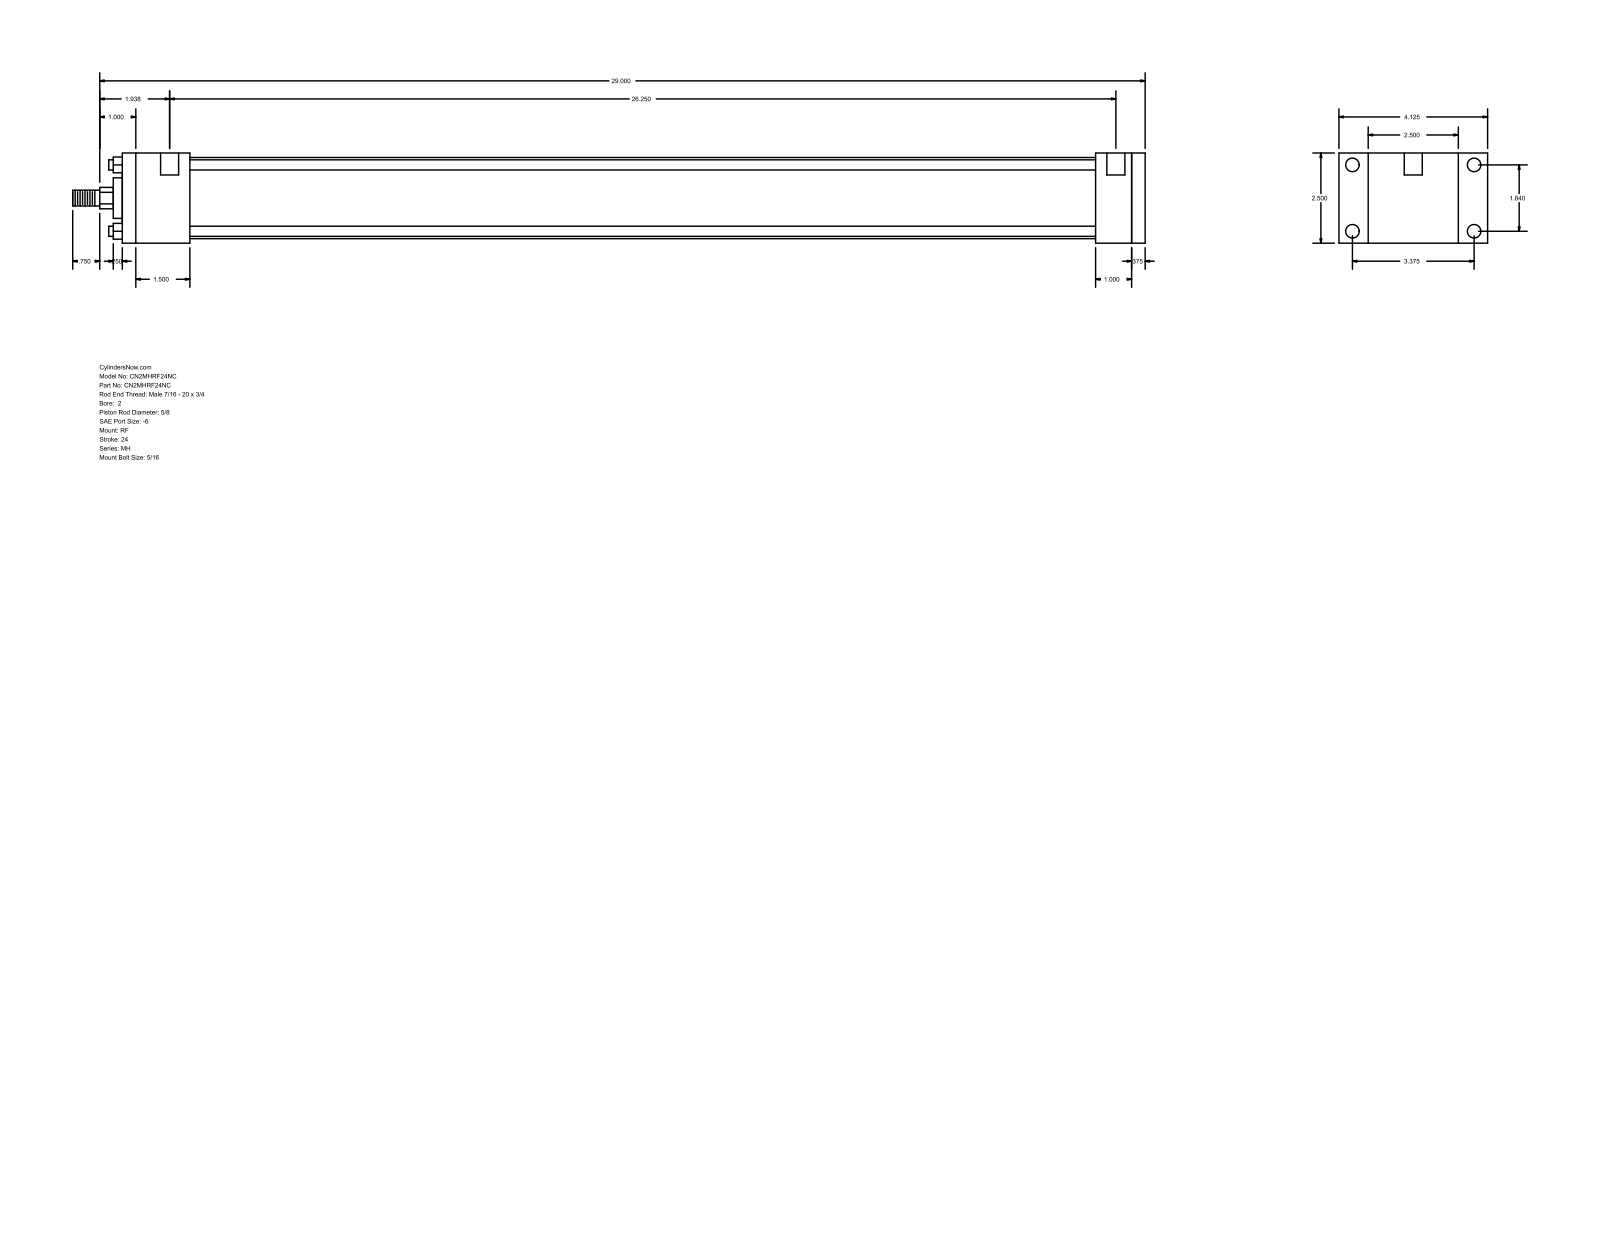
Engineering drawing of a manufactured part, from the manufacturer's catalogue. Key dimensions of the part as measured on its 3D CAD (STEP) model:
Part name (STEP PRODUCT): MH_RF__0200_0.625
STEP written by: GSSL Pune (CONFIG_CONTROL_DESIGN)
Units: millimetres
Bodies: 0 solids, 92 faces (64 planar, 28 cylindrical, 0 other)
Overall size (bounding box): 755.65 × 104.78 × 63.5
Round holes (diameter × count): ⌀5.56 ×4, ⌀9.53 ×4, ⌀12.7 ×2
Round bosses / shafts (diameter × count): ⌀7.14 ×4, ⌀57.15 ×1, ⌀28.57 ×1, ⌀15.88 ×1, ⌀11.11 ×1
Partial cylindrical surfaces — rounded edges, fillets, slot ends (radius × count): R7.54 ×1
Main face-to-face distances: 63.5, 720.72, 711.2, 9.52, 34.93, 47.62, 685.79, 638.17, 663.58, 673.1
Hole centre spacings: 46.74, 85.72, 97.63, 674.69, 3.18, 4.76, 666.75, 669.93
